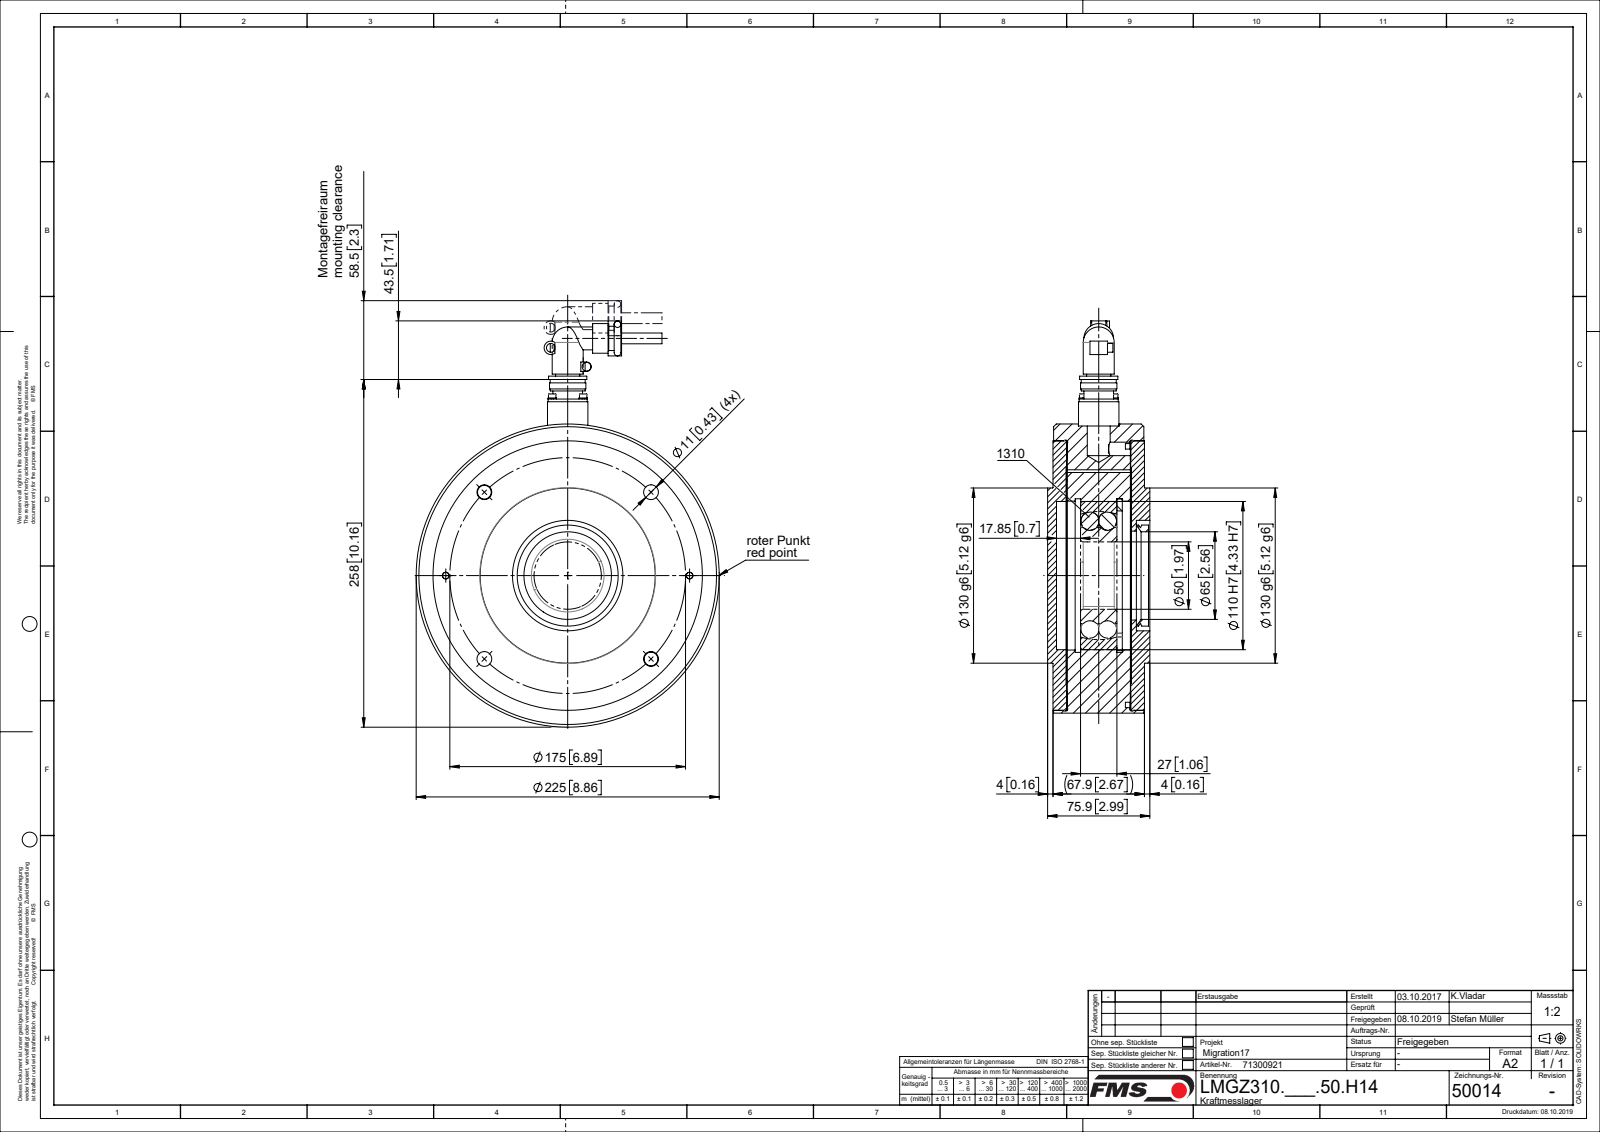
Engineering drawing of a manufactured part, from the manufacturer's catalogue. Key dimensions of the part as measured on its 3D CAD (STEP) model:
Part name (STEP PRODUCT): L50014; L4765504; TEIL1; L49152 (+8 more)
STEP written by: Mechanical Desktop 2007 (CONFIG_CONTROL_DESIGN)
Units: millimetres
Bodies: 20 solids, 406 faces (121 planar, 230 cylindrical, 55 other)
Overall size (bounding box): 301.5 × 225 × 75.9
Volume: 2 415 000 mm³ · Surface area: 392 936 mm²
Round holes (diameter × count): ⌀11 ×6, ⌀2.6 ×4, ⌀3.2 ×4, ⌀3.4 ×4, ⌀3.5 ×4, ⌀9 ×4, ⌀5 ×2, ⌀6.6 ×2, ⌀23 ×1, ⌀50 ×1, ⌀64 ×1, ⌀66 ×1
Round bosses / shafts (diameter × count): ⌀6.2 ×4, ⌀5.5 ×4, ⌀3 ×4, ⌀22 ×2, ⌀10 ×2, ⌀6.5 ×2, ⌀6 ×2, ⌀4.8 ×2
Partial cylindrical surfaces — rounded edges, fillets, slot ends (radius × count): R2.5 ×2, R3.5 ×1, R5 ×1, R81 ×1, R86 ×1
Main face-to-face distances: 9.7, 47.25, 10.45, 10.75, 47.45, 10.2, 57.45, 57.7, 47, 10
Hole centre spacings: 16.26, 23, 68.17, 87.5, 123.74, 164.45, 32.53, 90.5
